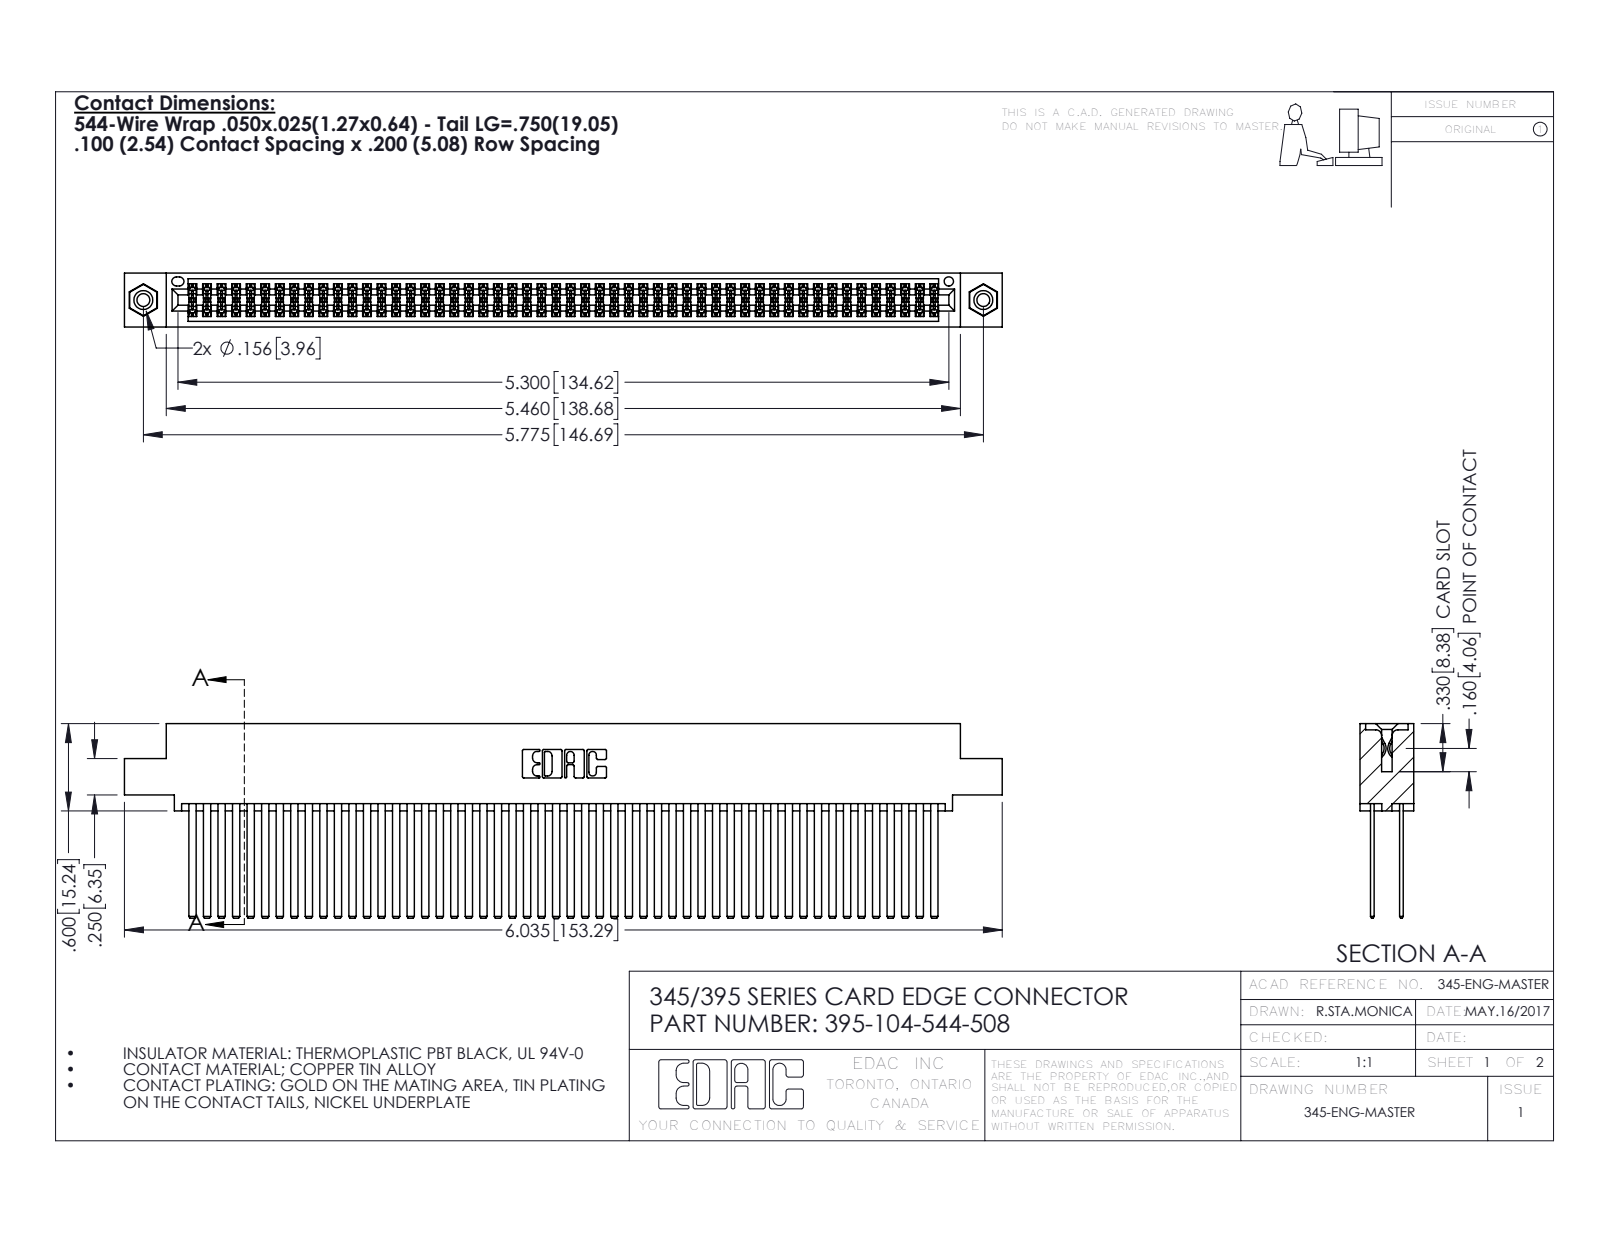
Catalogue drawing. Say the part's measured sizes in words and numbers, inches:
The part is named "345-250-001_345-250-003-102; 345-292-001_345-293-144; 395-104-544-508; 345 Part_0.110 Offset - 0.156 Dia-TI". Its 3-D file was written by "SolidWorks 2016 (CONFIG_CONTROL_DESIGN)". It is 107 solids with 4766 faces: 3132 planar, 1618 cylindrical and 16 other. Overall it measures 6.035 by 1.337 by 0.37 inches. Its volume is 0.998 cubic inches and its surface area 44.57 square inches. Round holes: 2 of diameter 0.089, 2 of diameter 0.125, 2 of diameter 0.156, 1 of diameter 0.064. Round bosses or shafts: 2 of diameter 0.155. Partial cylindrical surfaces (rounded edges, fillets, slot ends): 156 of radius 0.006, 22 of radius 0.01, 6 of radius 0.007, 6 of radius 0.031, 3 of radius 0.026, 2 of radius 0.014, 2 of radius 0.019, 2 of radius 0.022. The main face-to-face distances are 0.2, 0.025, 0.072, 0.098, 0.272, 0.298, 0.225, 0.175, 0.37, 0.05. The hole center spacings are 0.27, 5.539, 5.775.
